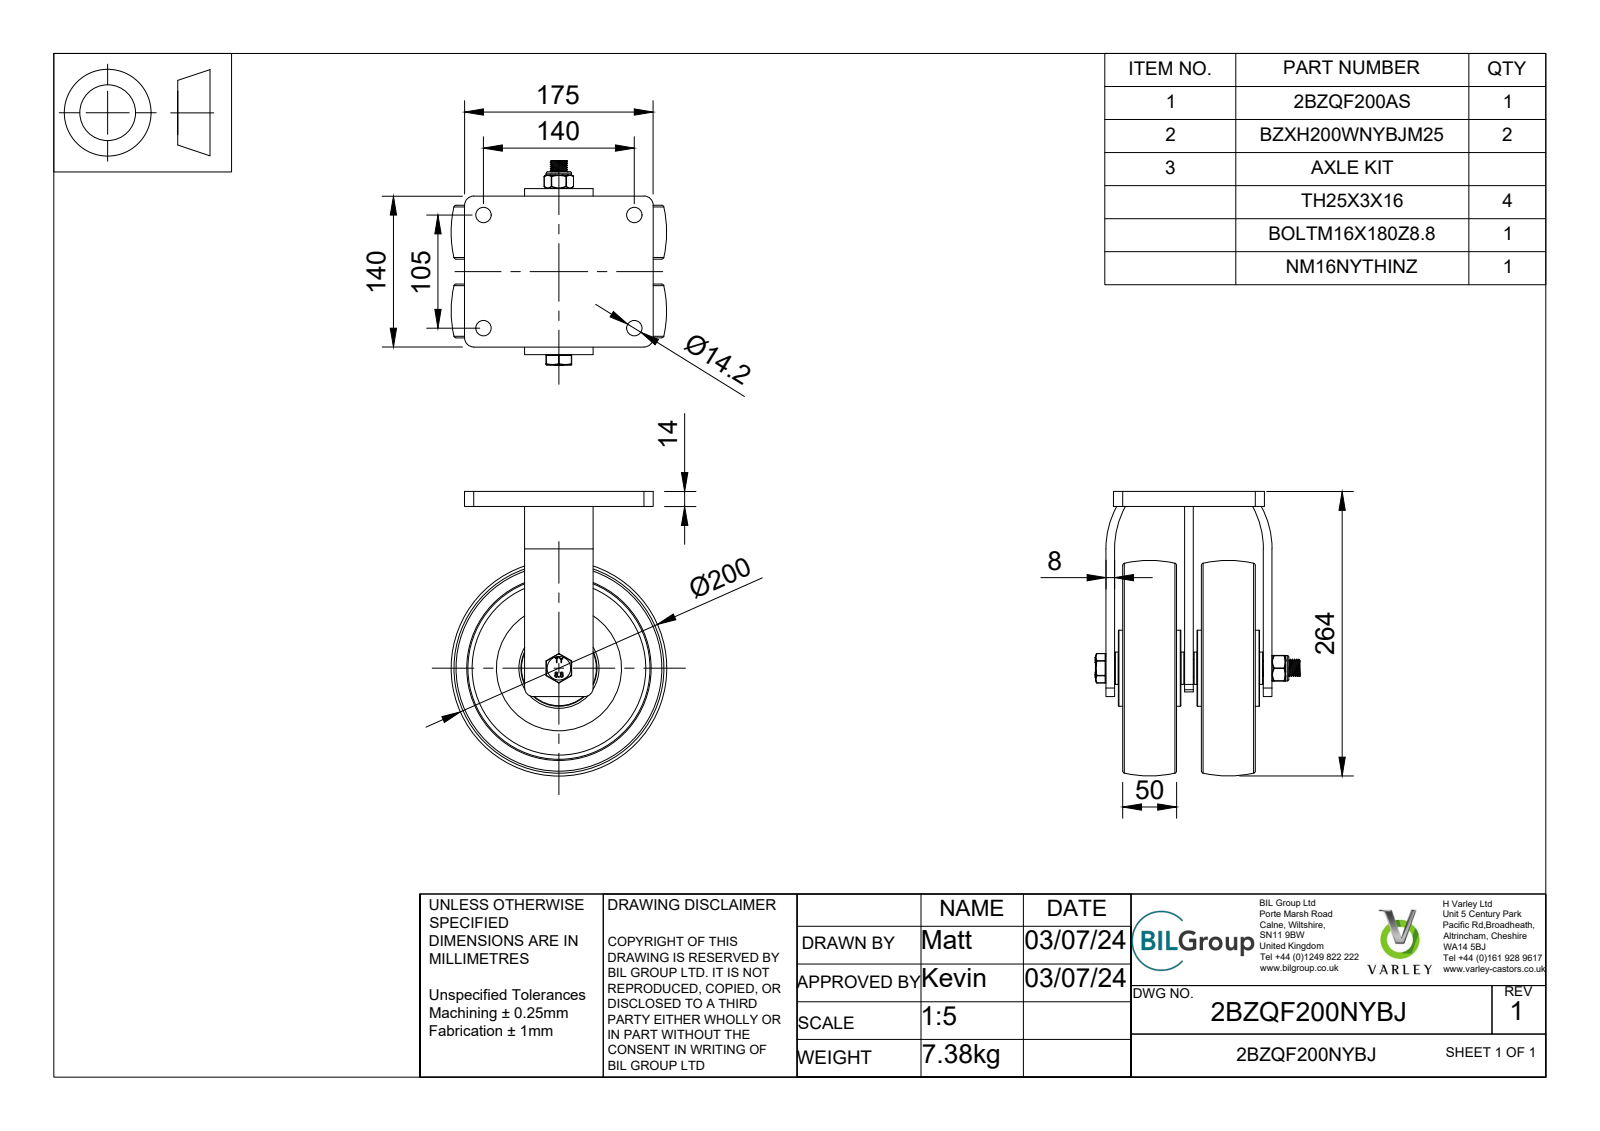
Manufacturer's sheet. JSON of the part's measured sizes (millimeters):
{"part_name": "2BZQF200NYBJ v3; 2BZQF200AS v1; 2BZQF200AS; FABRICATED STEEL BRACKET (+8 more)", "step_written_by": "Autodesk Translation Framework v13.14.0.145 (AUTOMOTIVE_DESIGN)", "units": "millimeters", "bodies": {"solids": 75, "faces": 1978, "planar": 630, "cylindrical": 247, "other": 1101}, "overall_size": [264, 200, 190.05], "volume_mm3": 2421000, "surface_area_mm2": 473405, "round_holes": [[14.2, 4], [16, 1], [16.2, 1], [18, 1], [25, 1], [26, 1], [32, 1], [32.4, 1], [34.1, 1], [39, 1], [40.4, 1], [41.5, 1]], "round_bosses_or_shafts": [[70.5, 1], [47, 1], [41.4, 1], [40.1, 1], [33.4, 1], [30, 1], [28.2, 1], [24.8, 1]], "partial_cylinders_radius": [[0.5, 18], [0.66, 4], [1.28, 4], [8.5, 4], [1.26, 2], [1.27, 2], [5, 2], [6.52, 2]], "face_to_face_distances": [73, 33, 48, 25, 40, 8, 15.5, 65.5, 7.5, 57.5], "hole_center_spacings": [105, 140, 175]}
